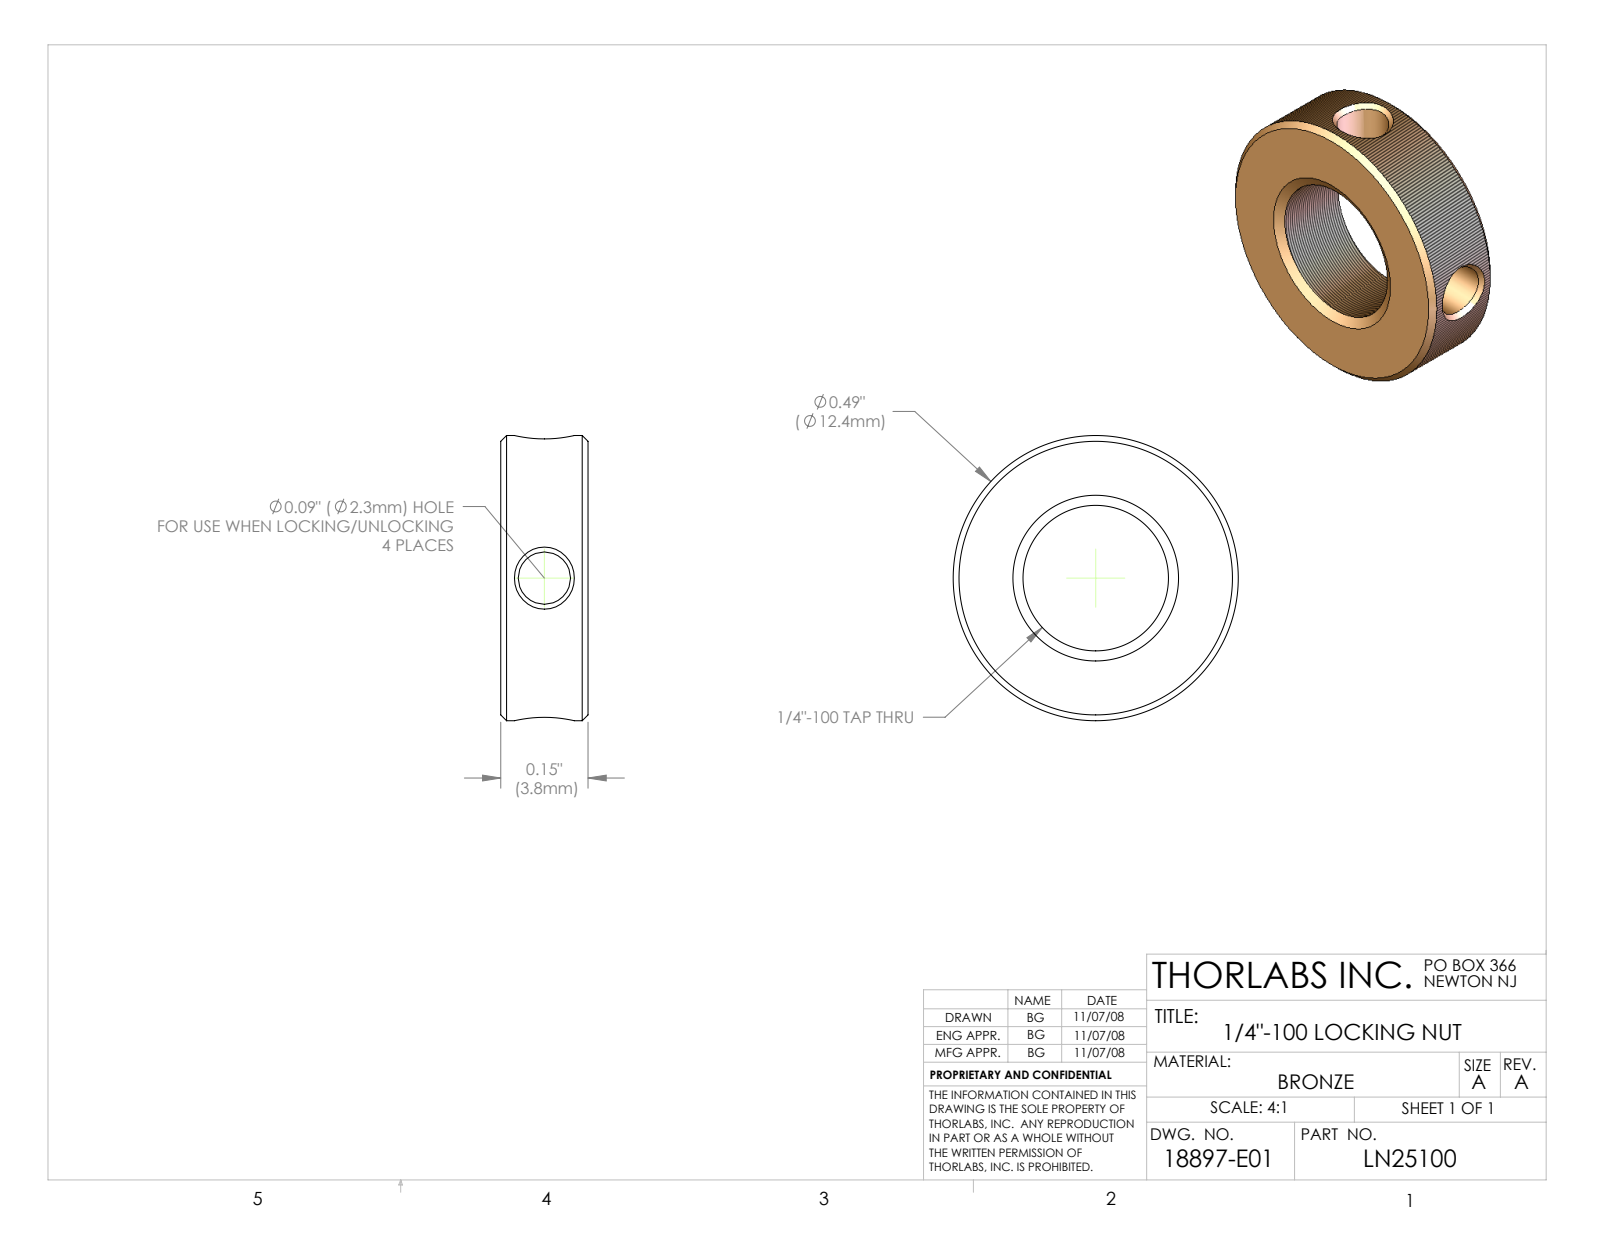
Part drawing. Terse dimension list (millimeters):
name: 18897-E0W
written by: SolidWorks 2007 (AUTOMOTIVE_DESIGN)
unit: mm
bodies: 1 solid, 34 faces (6 planar, 12 cylindrical, 16 other)
size: 12.45 × 12.45 × 3.81
volume: 296 mm³; area: 453 mm²
holes: 2× ⌀2.29, 1× ⌀6.35
bosses: 1× ⌀12.45
face distances: 3.8, 7.36
